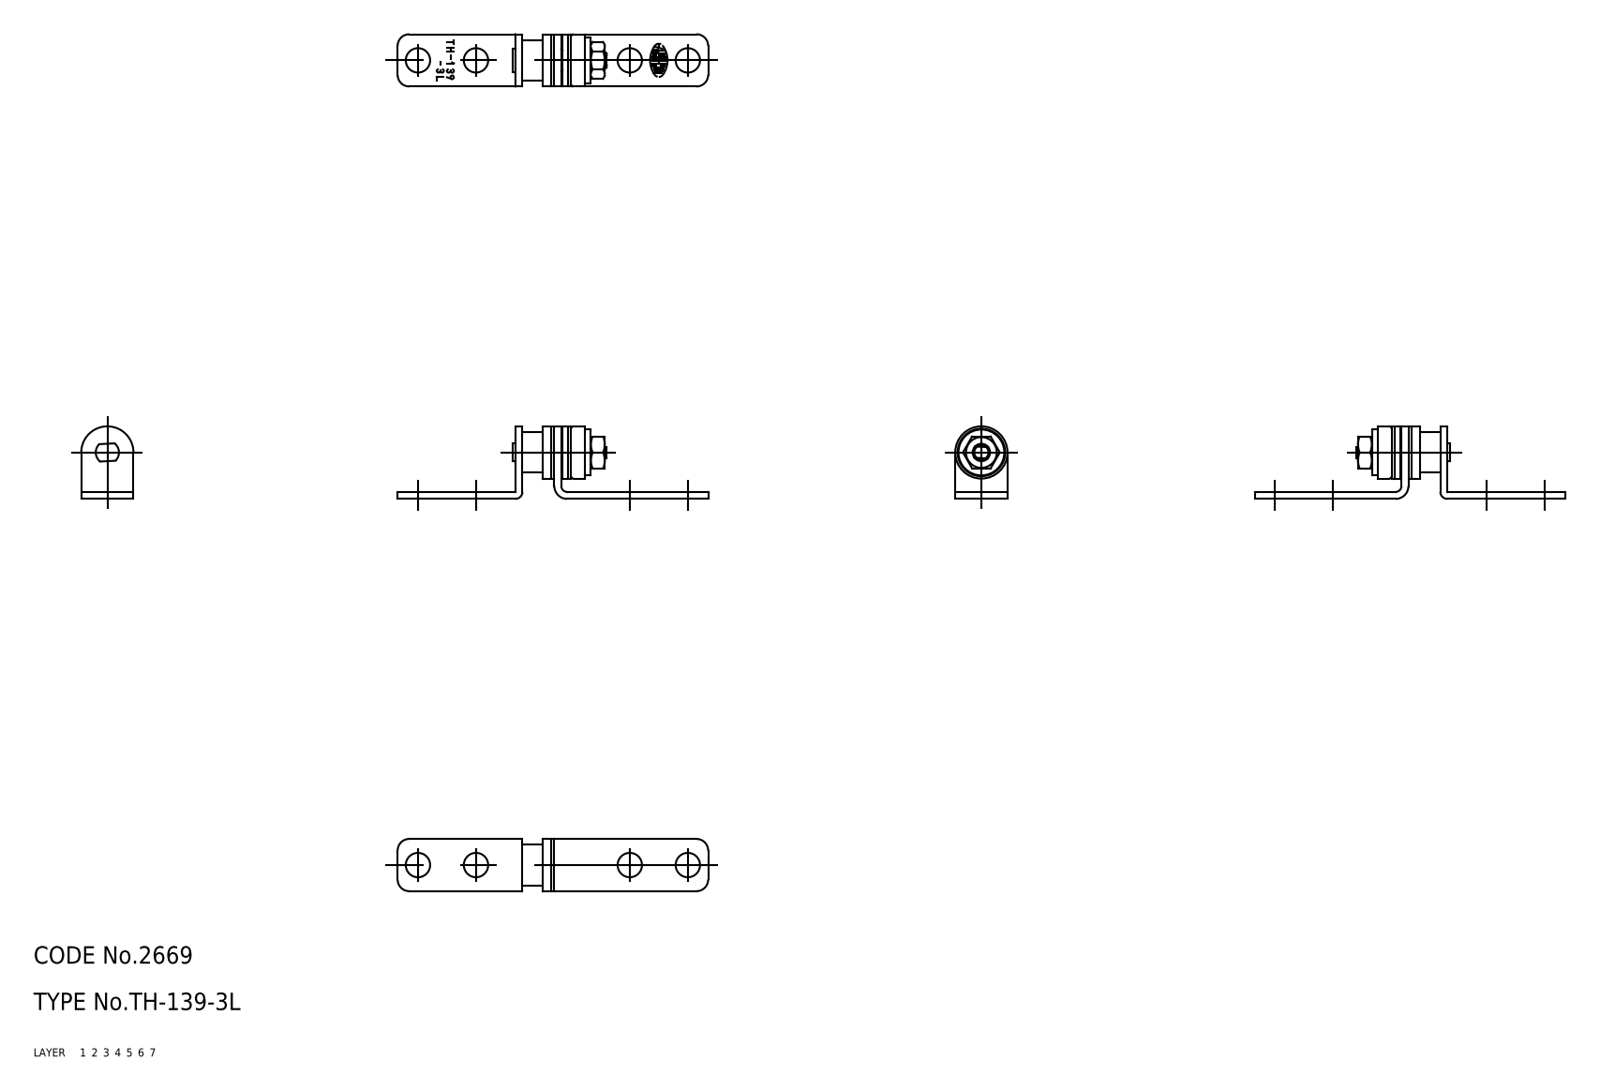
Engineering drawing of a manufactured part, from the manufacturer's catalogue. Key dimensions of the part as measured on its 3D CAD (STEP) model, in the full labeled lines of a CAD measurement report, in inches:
Part name (STEP PRODUCT): 67115570; 67115583; 67115596; 67115609 (+7 more)
STEP written by: CADfix (AUTOMOTIVE_DESIGN)
Units: inches
Bodies: 11 solids, 113 faces (0 planar, 0 cylindrical, 113 other)
Overall size (bounding box): 2.106 × 0.501 × 0.37
Volume: 0.078 in³ · Surface area: 4.095 in²
